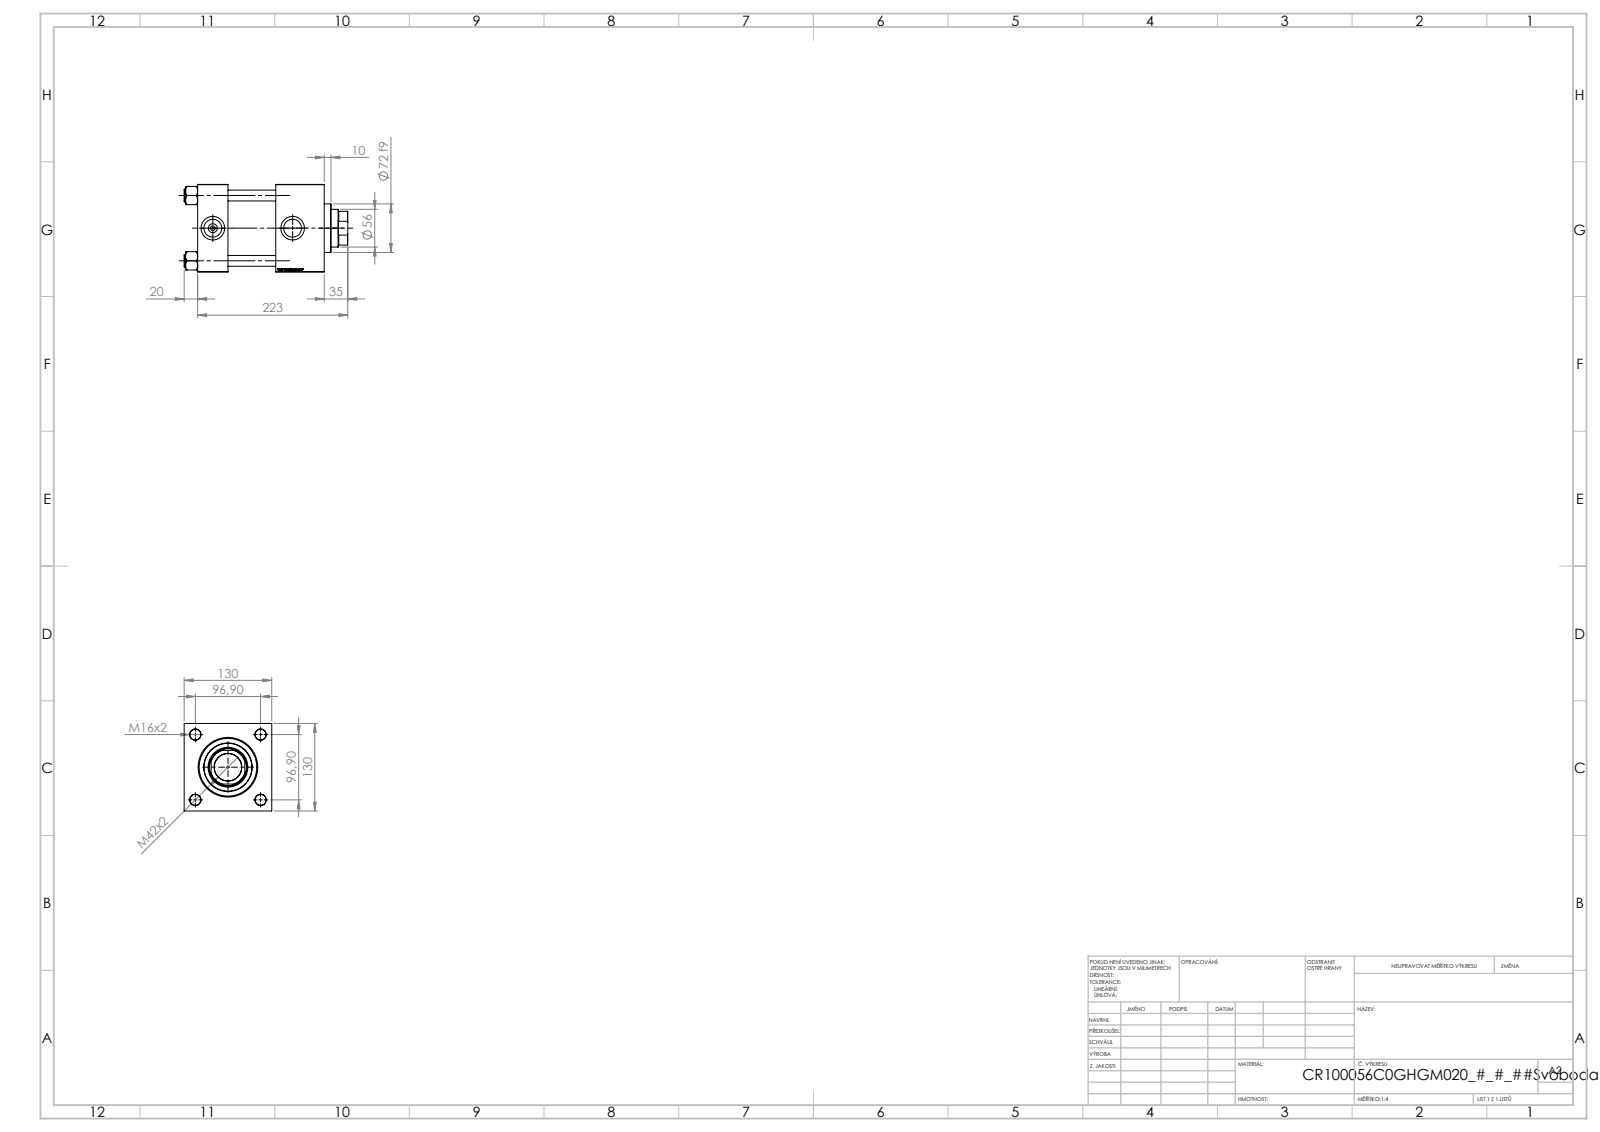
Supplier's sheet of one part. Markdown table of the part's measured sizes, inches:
| quantity | value |
| --- | --- |
| part name | V215CR_C_Body; V215_VC_A; V215CR_VCP_C; V215CR_C_TYCINKA (+1 more) |
| STEP written by | SolidWorks 2019 (CONFIG_CONTROL_DESIGN) |
| units | inches |
| bodies | 11 solids, 1196 faces (574 planar, 86 cylindrical, 536 other) |
| overall size | 9.567 × 5.118 × 5.118 |
| volume | 151 in³ |
| surface area | 516.7 in² |
| round holes (diameter × count) | 0.63 × 4, 0.276 × 2, 1.041 × 2, 1.378 × 2, 1.594 × 1, 2.205 × 1, 2.323 × 1, 2.992 × 1, 3.366 × 1, 3.937 × 1 |
| round bosses / shafts (diameter × count) | 0.748 × 4, 4.173 × 1, 2.835 × 1 |
| partial cylindrical surfaces (radius × count) | 1.063 × 1 |
| main face-to-face distances | 5.118, 1.772, 7.402, 5.63, 4.567, 2.795, 2.835, 0.787, 2.008, 3.78 |
| hole center spacings | 2.698, 3.815, 5.395, 4.665 |
